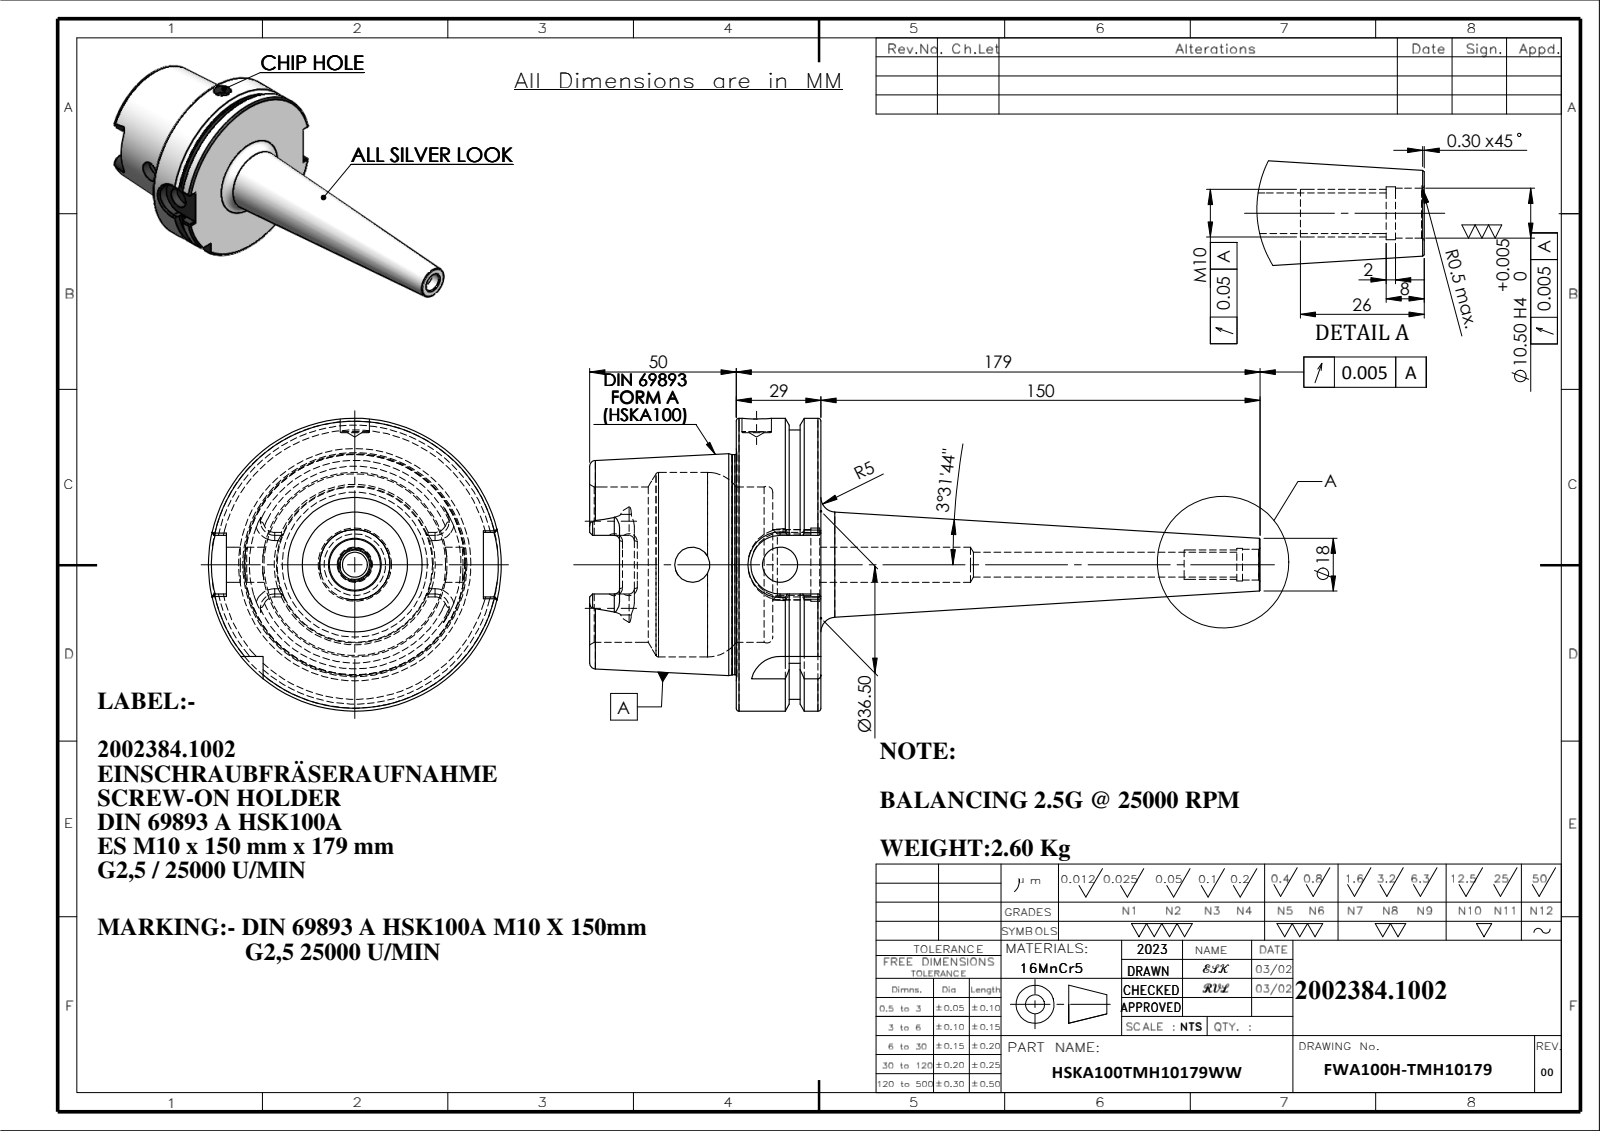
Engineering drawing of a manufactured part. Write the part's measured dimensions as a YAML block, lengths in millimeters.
part_name: "91100A-ES8M10150"
step_written_by: "SolidWorks 2018 (CONFIG_CONTROL_DESIGN)"
units: millimeters
bodies: {solids: 1, faces: 174, planar: 50, cylindrical: 52, other: 72}
overall_size: [228.95, 100, 100]
volume: 333419
surface_area: 66233
round_holes:
  - {diameter: 12, count: 3}
  - {diameter: 8.5, count: 1}
  - {diameter: 10, count: 1}
  - {diameter: 10.5, count: 1}
  - {diameter: 11.1, count: 1}
  - {diameter: 21, count: 1}
  - {diameter: 25, count: 1}
  - {diameter: 53, count: 1}
  - {diameter: 63, count: 1}
round_bosses_or_shafts:
  - {diameter: 100, count: 1}
  - {diameter: 92, count: 1}
  - {diameter: 75.16, count: 1}
partial_cylinders:
  - {radius: 1.8, count: 6}
  - {radius: 4.88, count: 4}
  - {radius: 10, count: 2}
  - {radius: 11, count: 1}
face_to_face_distances: [28.95, 12.5, 16.45, 50, 62.5, 78.95, 71.87, 21.87, 9.37, 7.08]
hole_center_spacings: [30]
